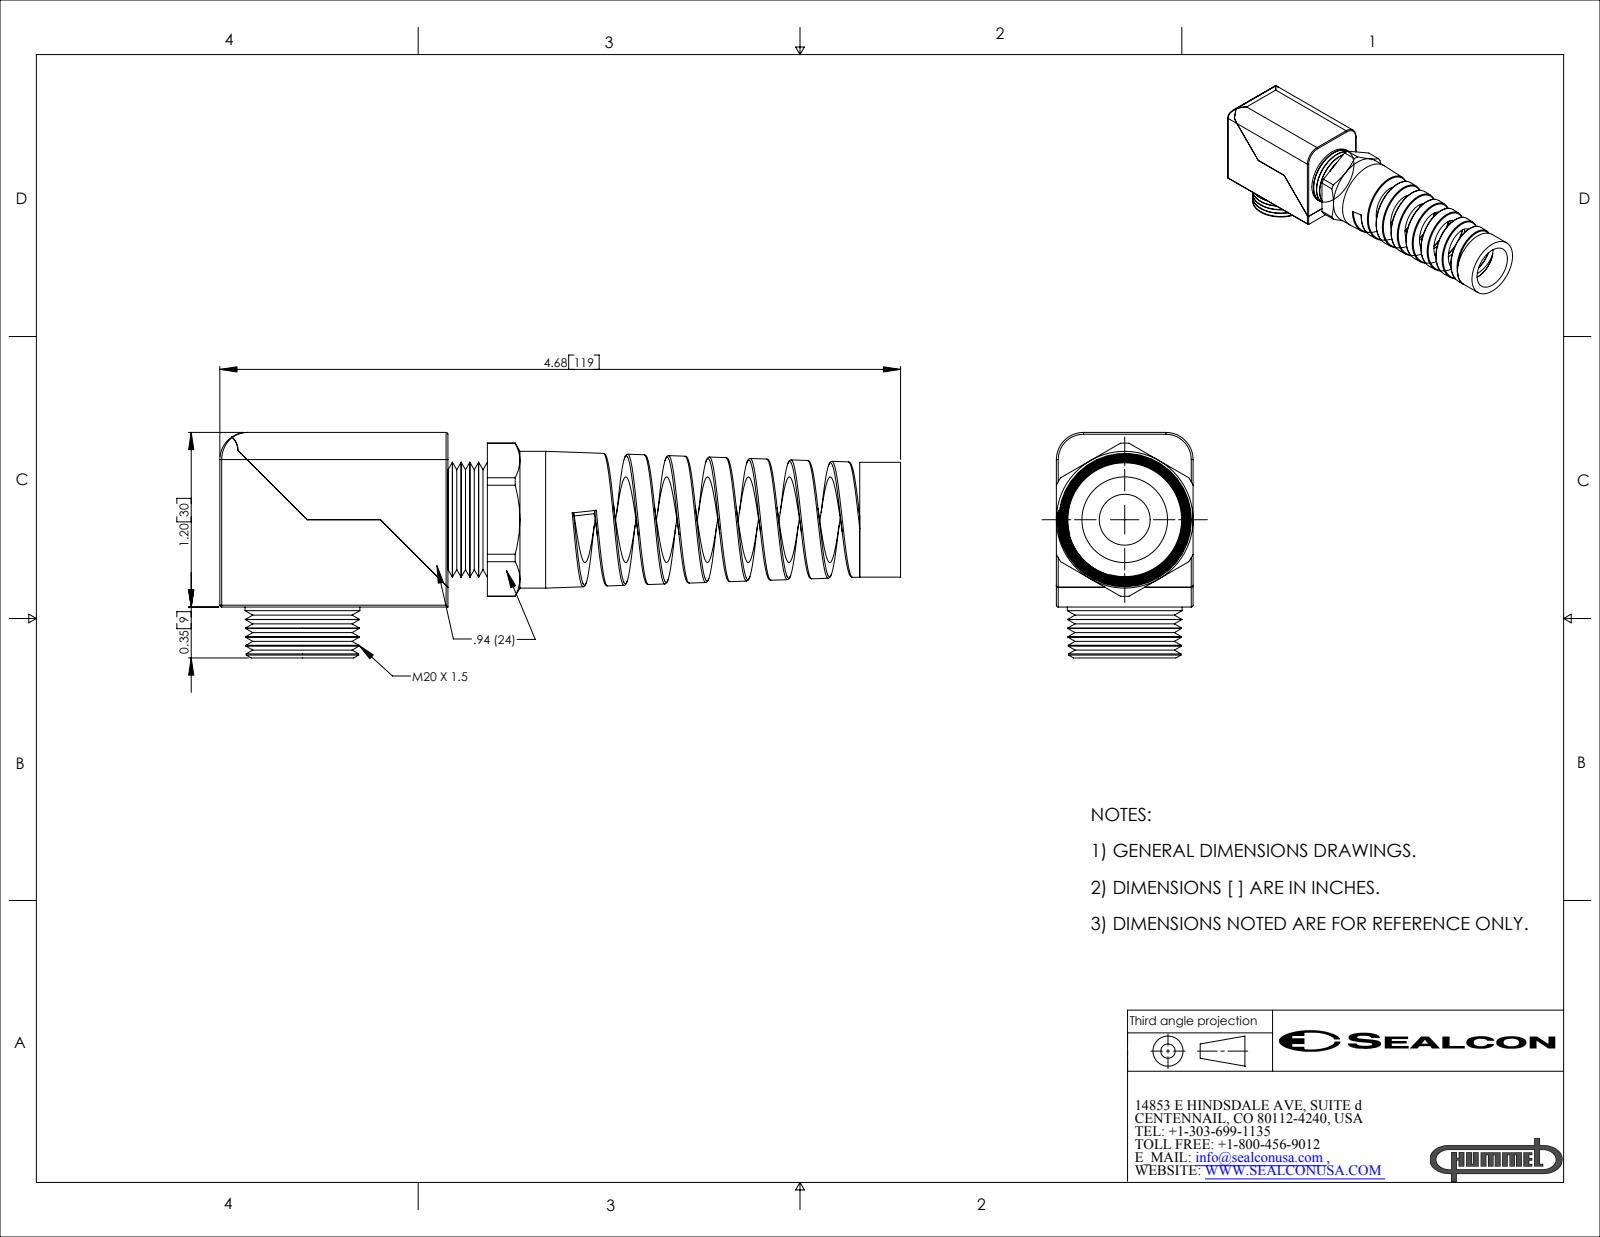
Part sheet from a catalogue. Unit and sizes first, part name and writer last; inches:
Units: inches
Overall size (bounding box): 4.68 × 1.55 × 0.94
Round holes (diameter × count): ⌀0.35 ×2, ⌀0.589 ×1, ⌀0.632 ×1
Round bosses / shafts (diameter × count): ⌀0.94 ×1, ⌀0.79 ×1, ⌀0.789 ×1
Partial cylindrical surfaces — rounded edges, fillets, slot ends (radius × count): R0.013 ×8, R0.187 ×3, R0.124 ×1, R0.526 ×1
Main face-to-face distances: 0.94, 0.6, 0.356, 1.2, 1.568, 2.831, 4.399, 2.56, 0.271, 1.839
Volume: 2.449 in³ · Surface area: 29.85 in²
Bodies: 3 solids, 183 faces (31 planar, 63 cylindrical, 89 other)
Part name (STEP PRODUCT): EF20MR-GY
STEP written by: SolidWorks 2007 (CONFIG_CONTROL_DESIGN)
